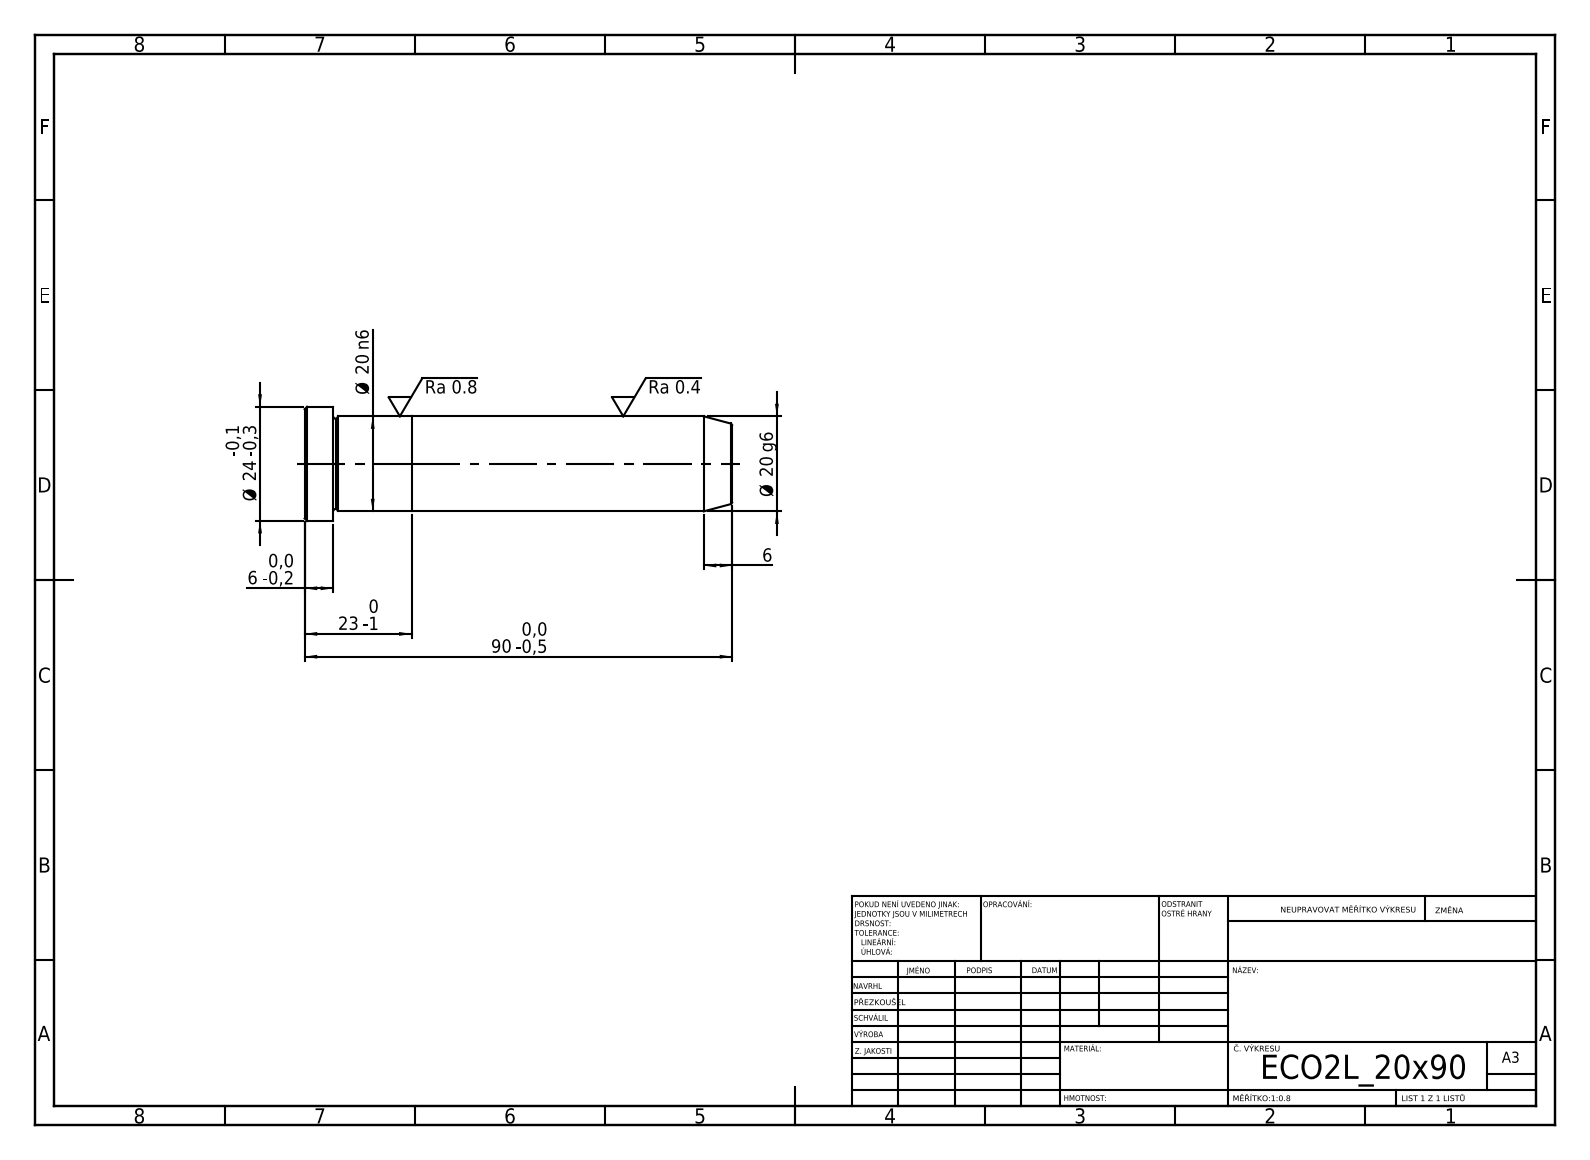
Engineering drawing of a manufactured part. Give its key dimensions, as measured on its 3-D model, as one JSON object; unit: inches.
{"step_written_by": "SolidWorks 2019 (CONFIG_CONTROL_DESIGN)", "units": "inches", "bodies": {"solids": 2, "faces": 21, "planar": 5, "cylindrical": 6, "other": 10}, "overall_size": [3.543, 0.945, 0.945], "volume_in3": 1.756, "surface_area_in2": 11.09, "round_bosses_or_shafts": [[0.945, 1], [0.787, 1]], "face_to_face_distances": [0.886, 2.657, 3.543, 3.307, 0.65, 0.236]}
